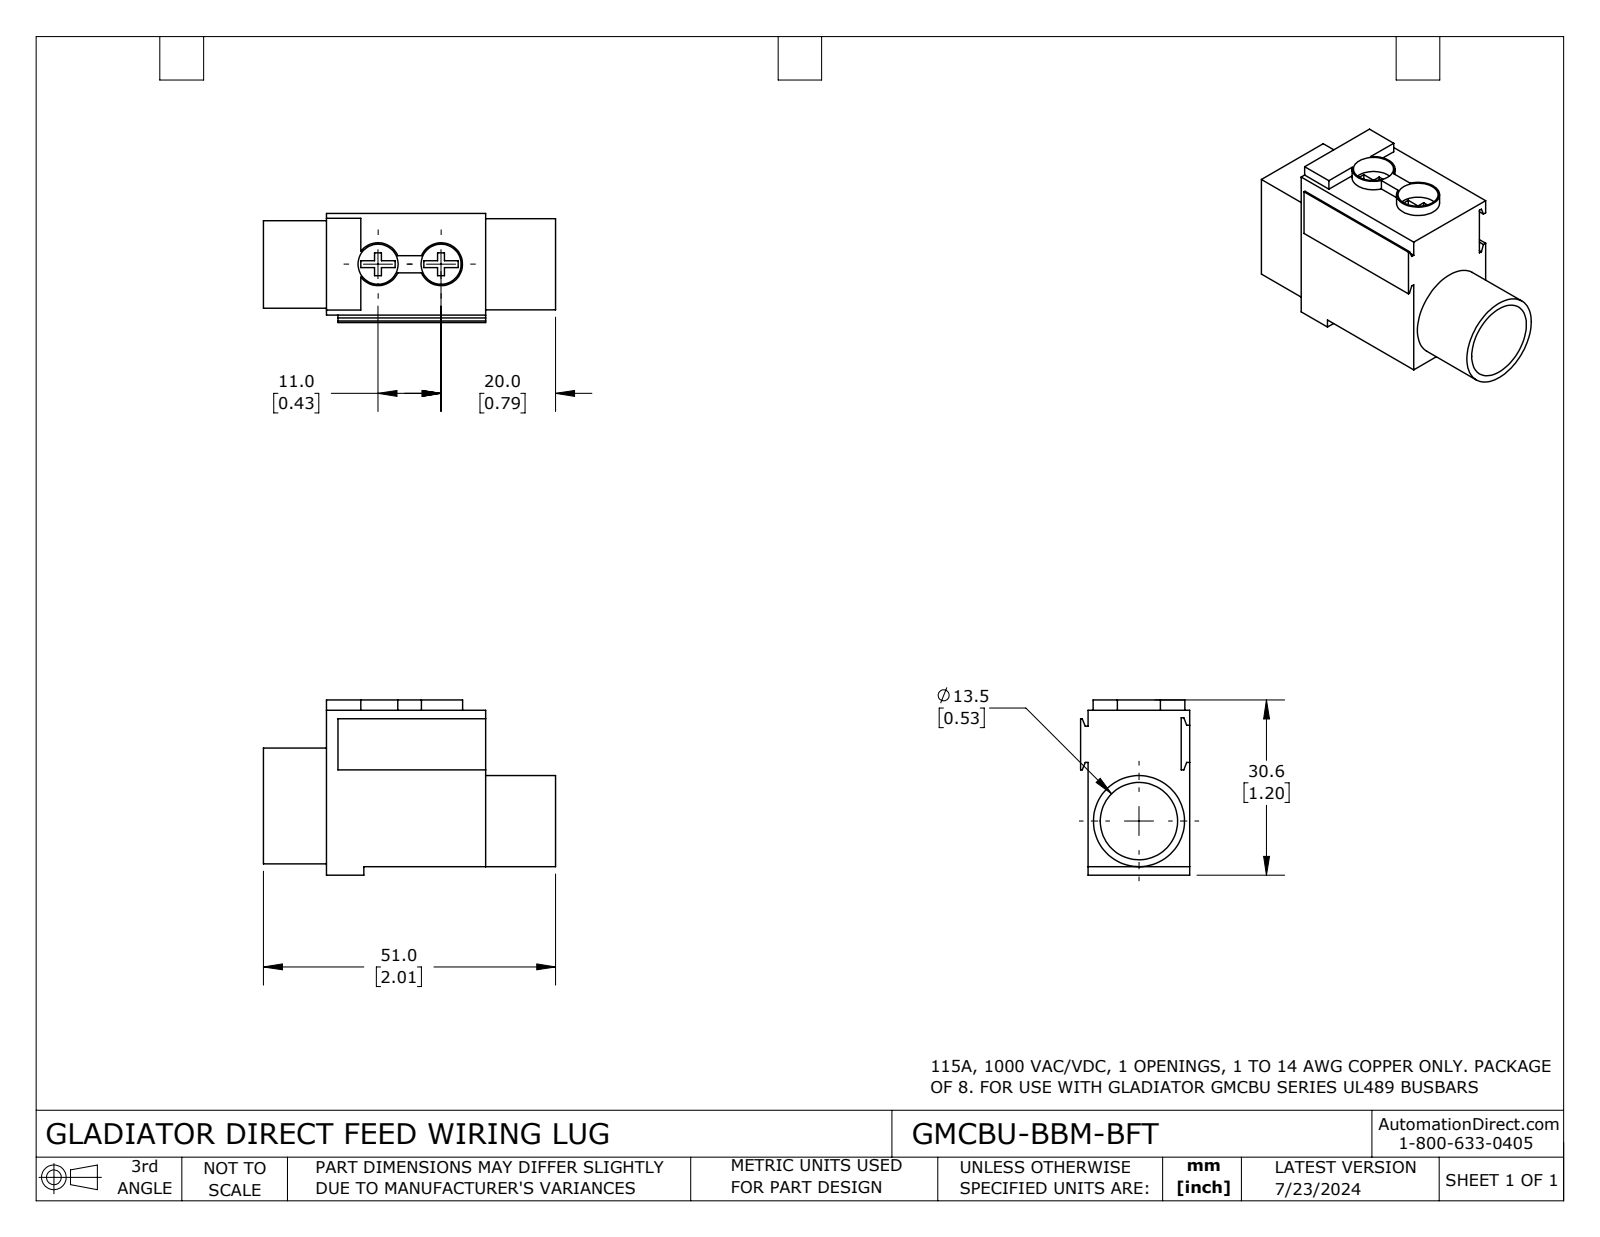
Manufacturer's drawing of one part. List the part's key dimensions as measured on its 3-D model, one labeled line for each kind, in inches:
Part name (STEP PRODUCT): GMCBU-BBM-BFT
STEP written by: SolidWorks 2023 (CONFIG_CONTROL_DESIGN)
Units: inches
Bodies: 1 solid, 85 faces (71 planar, 14 cylindrical, 0 other)
Overall size (bounding box): 2.008 × 1.205 × 0.75
Volume: 0.931 in³ · Surface area: 10.58 in²
Round holes (diameter × count): ⌀0.276 ×2, ⌀0.531 ×1
Round bosses / shafts (diameter × count): ⌀0.626 ×1, ⌀0.295 ×1
Partial cylindrical surfaces — rounded edges, fillets, slot ends (radius × count): R0.148 ×1
Main face-to-face distances: 0.699, 1.094, 0.059, 1.075, 0.051, 0.649, 0.64, 0.691, 0.75, 0.097
Hole centre spacings: 0.433
